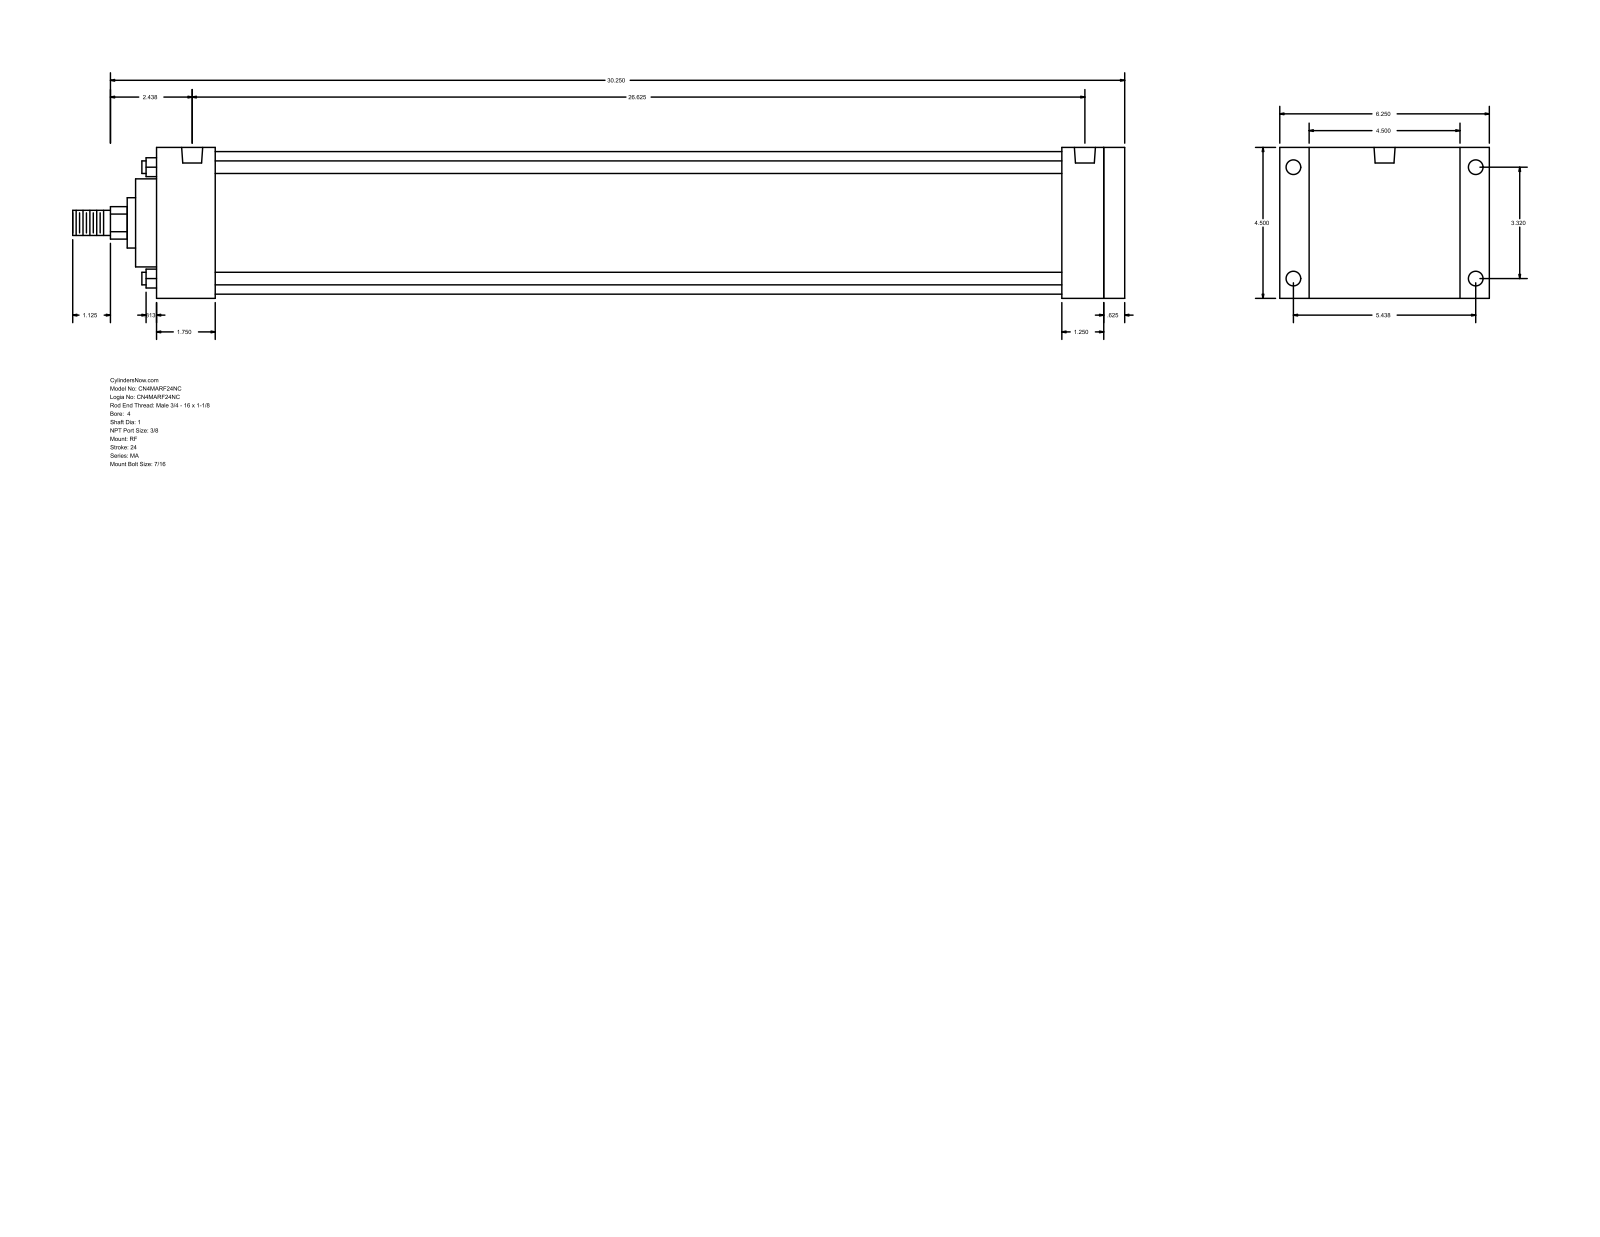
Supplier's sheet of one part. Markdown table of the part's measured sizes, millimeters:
| quantity | value |
| --- | --- |
| part name | MA_RF__0400_1 |
| STEP written by | GSSL Pune (CONFIG_CONTROL_DESIGN) |
| units | millimeters |
| bodies | 0 solids, 94 faces (65 planar, 29 cylindrical, 0 other) |
| overall size | 796.92 × 158.75 × 114.3 |
| round holes (diameter × count) | 11.11 × 8, 15.93 × 2 |
| round bosses / shafts (diameter × count) | 9.53 × 4, 107.95 × 1, 66.67 × 1, 38.1 × 1, 25.4 × 1, 19.05 × 1 |
| partial cylindrical surfaces (radius × count) | 12.29 × 1 |
| main face-to-face distances | 114.3, 733.43, 15.87, 717.56, 47.62, 22.23, 136.53, 685.81, 31.75, 44.46 |
| hole center spacings | 84.32, 138.12, 161.82, 666.75, 4.76, 4.77, 671.51, 671.52 |
